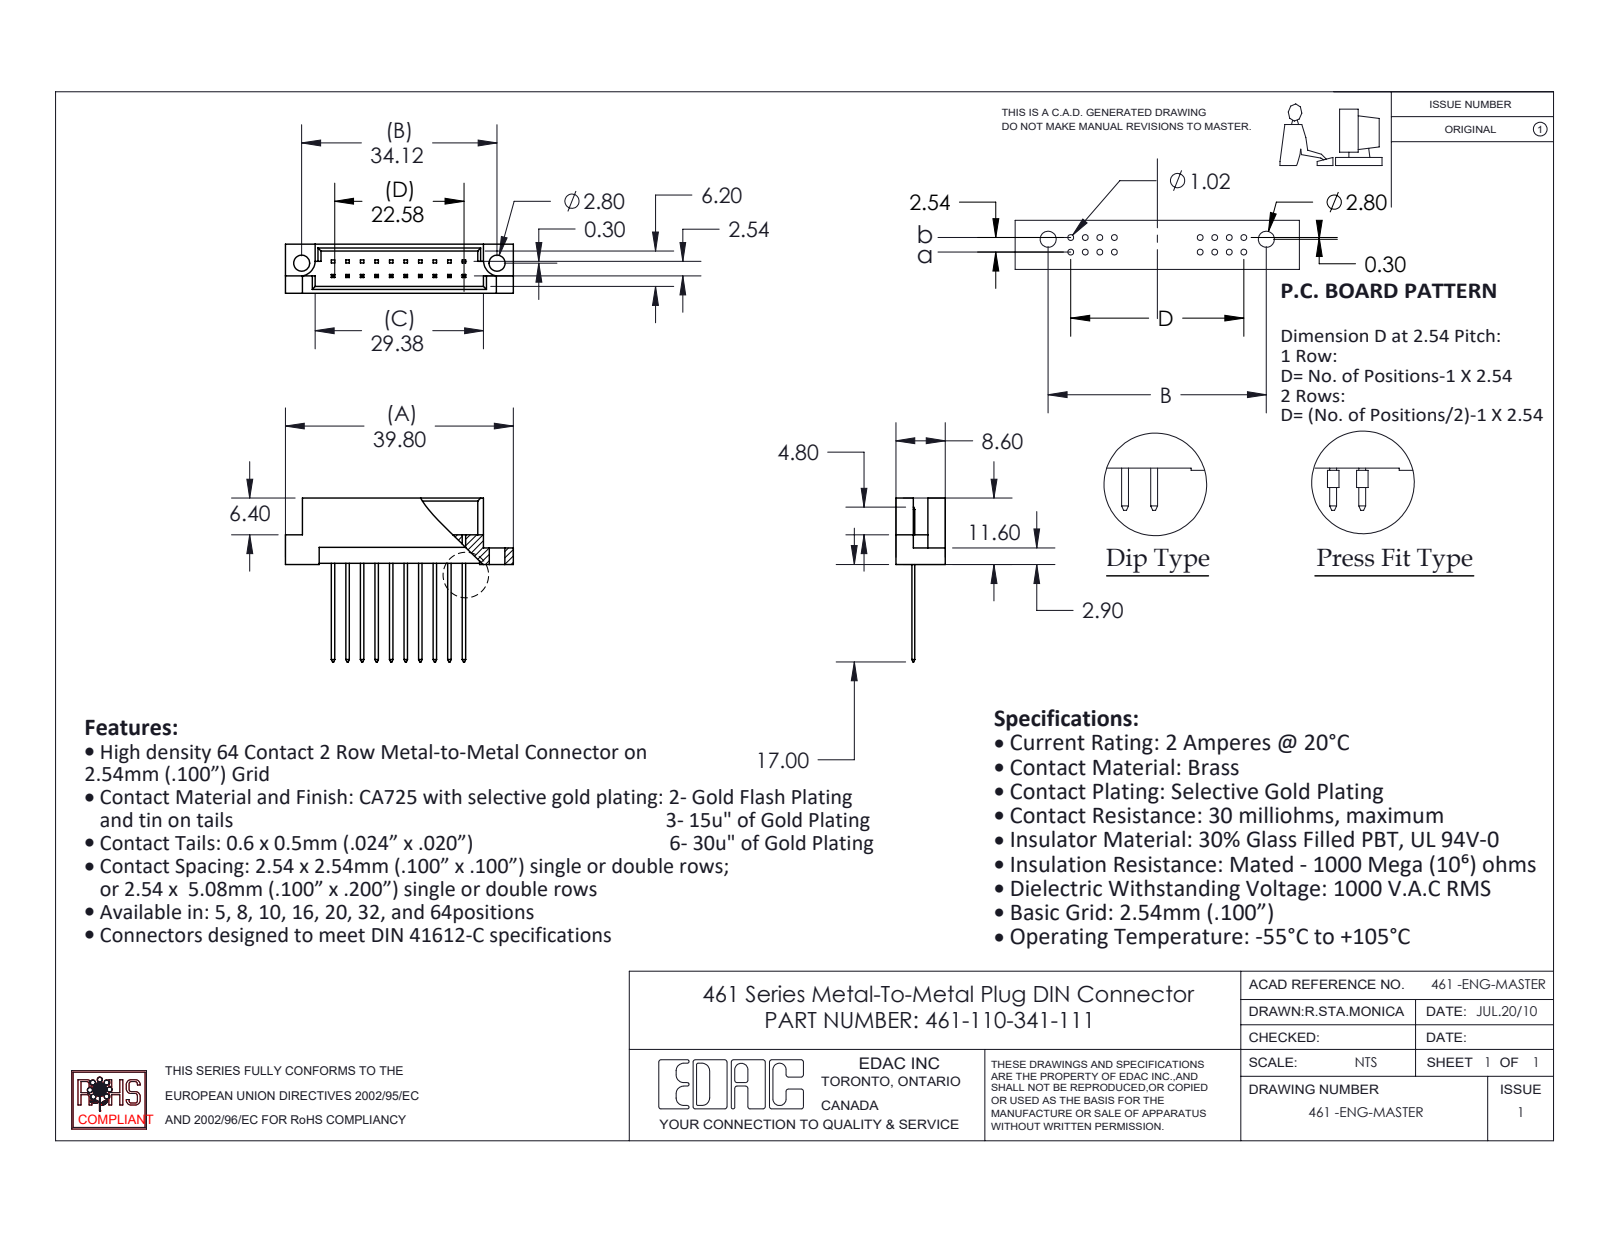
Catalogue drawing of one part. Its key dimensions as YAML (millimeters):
part_name: "461-110-341-111; 461-290_41; 461 Part_20"
step_written_by: "SolidWorks 2020 (CONFIG_CONTROL_DESIGN)"
units: millimeters
bodies: {solids: 11, faces: 268, planar: 262, cylindrical: 6, other: 0}
overall_size: [39.8, 28.6, 8.6]
volume: 1985
surface_area: 2928
round_holes:
  - {diameter: 2.8, count: 2}
partial_cylinders:
  - {radius: 2.8, count: 2}
face_to_face_distances: [1.2, 7.4, 8.6, 2.54, 6.2, 3.28, 5.32, 2.08, 4.12, 2.78]
hole_center_spacings: [34.12]
